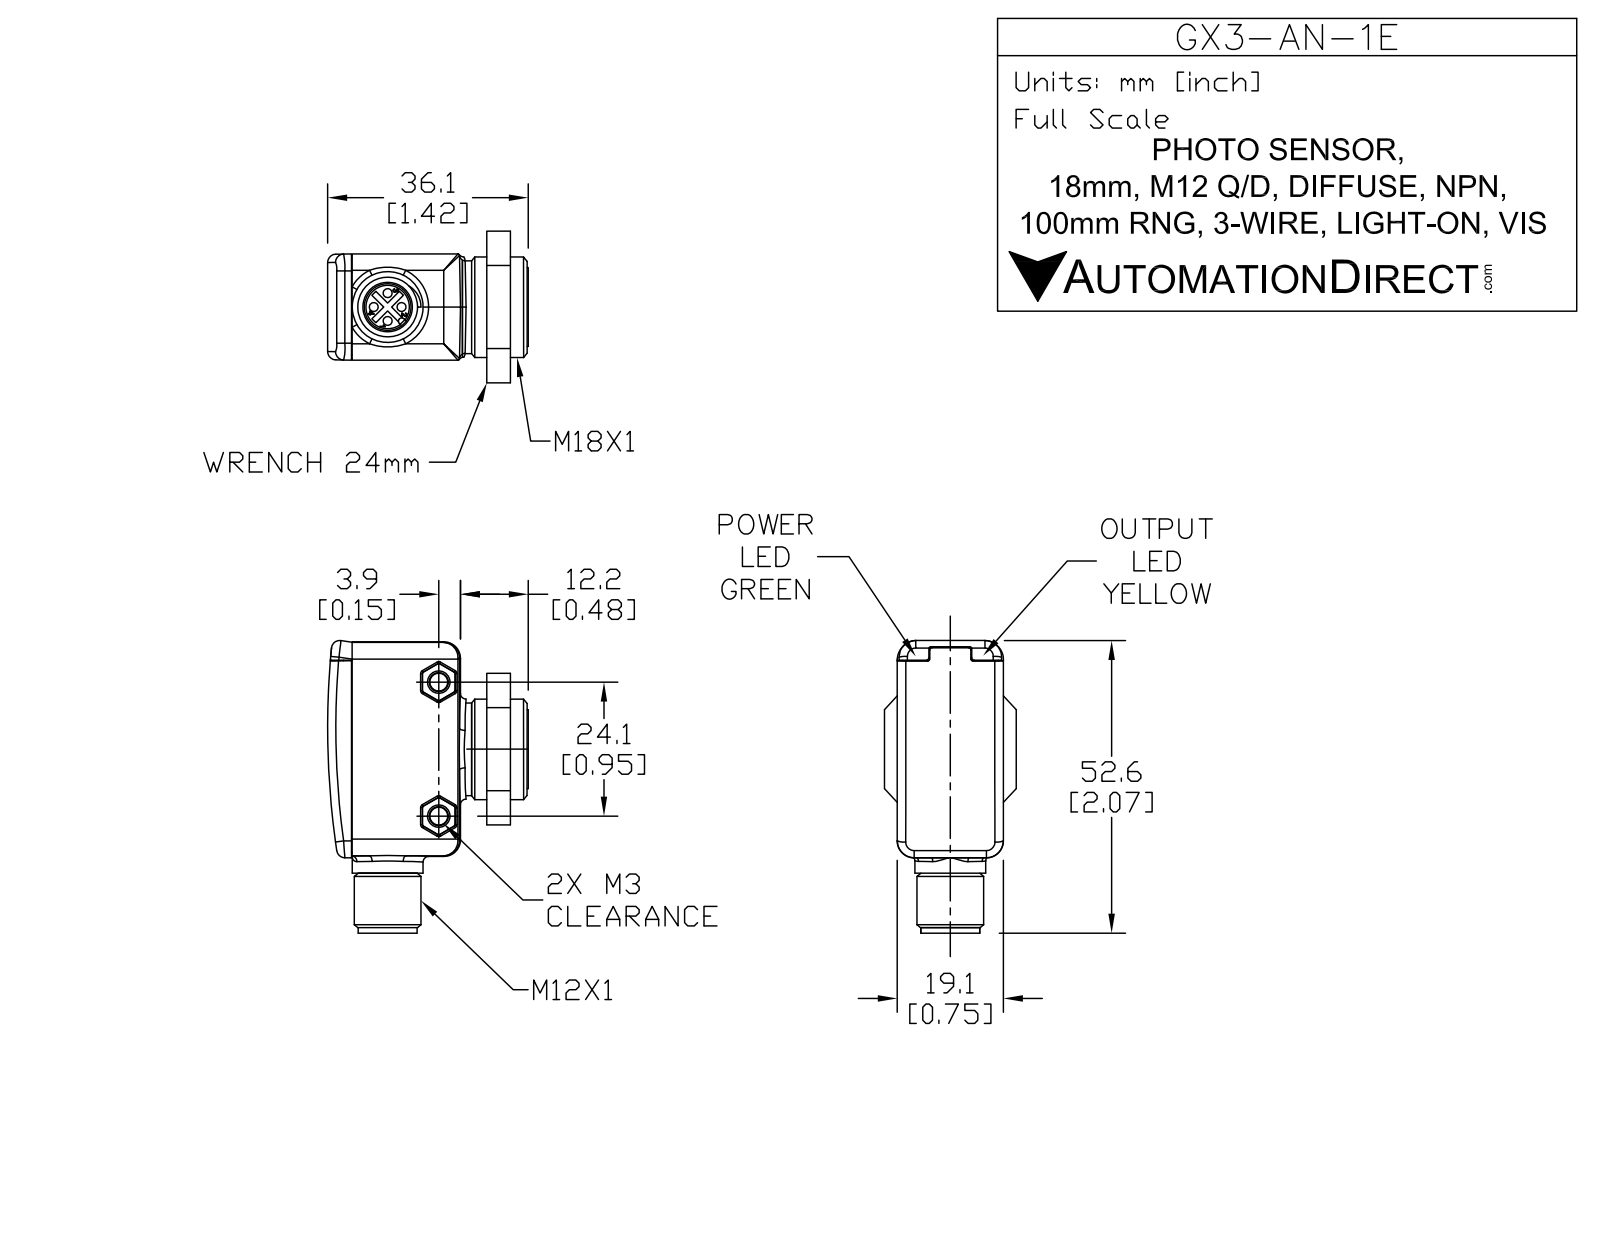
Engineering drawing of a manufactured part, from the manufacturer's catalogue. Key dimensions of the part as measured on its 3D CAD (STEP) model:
Part name (STEP PRODUCT): GX3-AN-1E
STEP written by: SolidWorks 2013 (AUTOMOTIVE_DESIGN)
Units: millimetres
Bodies: 1 solid, 107 faces (60 planar, 33 cylindrical, 14 other)
Overall size (bounding box): 52.66 × 36.1 × 23.85
Volume: 21 253 mm³ · Surface area: 6 452 mm²
Round holes (diameter × count): ⌀3.2 ×2, ⌀8.36 ×1
Round bosses / shafts (diameter × count): ⌀18 ×1, ⌀17.5 ×1, ⌀14.2 ×1, ⌀12.68 ×1, ⌀11.55 ×1, ⌀10.6 ×1
Partial cylindrical surfaces — rounded edges, fillets, slot ends (radius × count): R1.5 ×8, R1 ×4, R139.57 ×1
Main face-to-face distances: 19.1, 7.2, 2.12, 9.32, 19.2, 5, 2.88, 12.2, 38.8, 5.95
Hole centre spacings: 24.1
